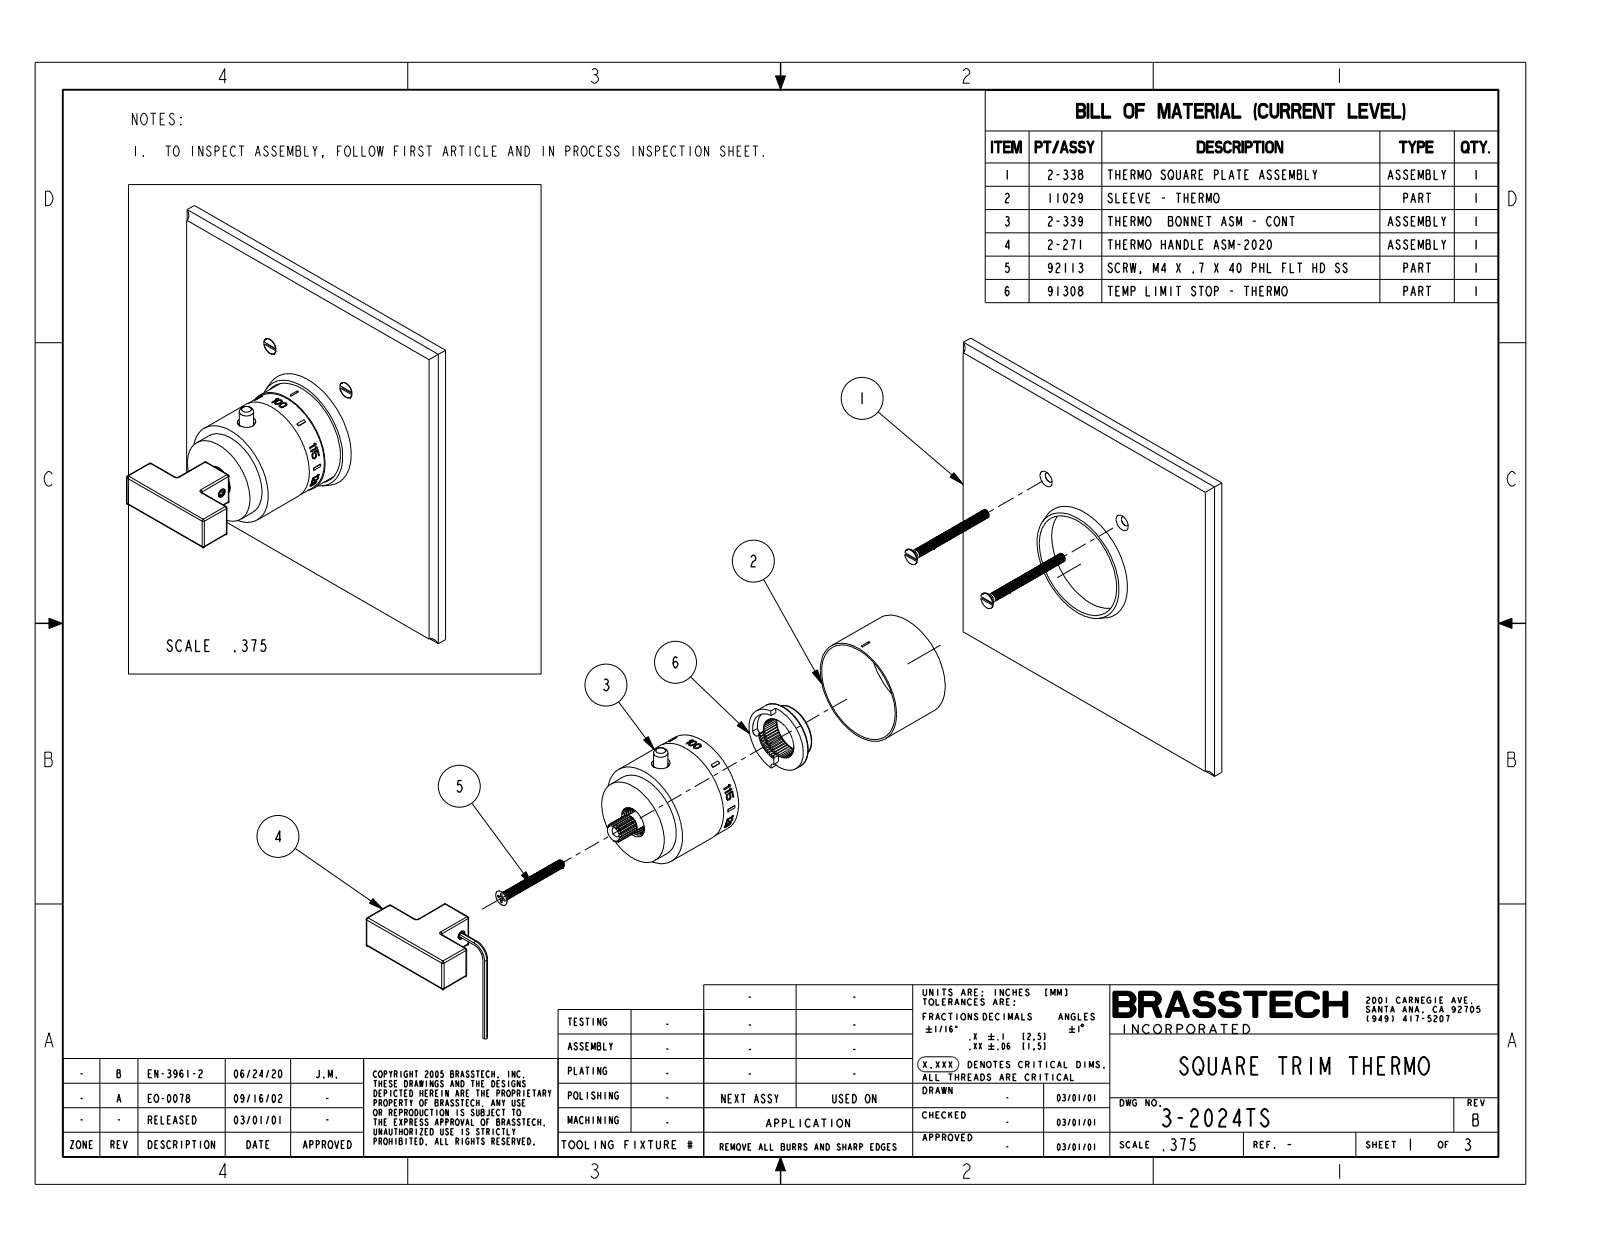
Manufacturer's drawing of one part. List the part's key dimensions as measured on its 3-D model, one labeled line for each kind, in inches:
Part name (STEP PRODUCT): 3-2024TS
STEP written by: CREO PARAMETRIC BY PTC INC, 2018400 (CONFIG_CONTROL_DESIGN)
Units: inches
Bodies: 1 solid, 422 faces (341 planar, 61 cylindrical, 20 other)
Overall size (bounding box): 6.5 × 6.5 × 4.024
Volume: 20.62 in³ · Surface area: 112.5 in²
Round bosses / shafts (diameter × count): ⌀1.97 ×1, ⌀1.94 ×1, ⌀1.929 ×1, ⌀1.615 ×1, ⌀0.4 ×1, ⌀0.26 ×1, ⌀0.067 ×1
Partial cylindrical surfaces — rounded edges, fillets, slot ends (radius × count): R0.03 ×22, R0.125 ×4, R0.969 ×1
Main face-to-face distances: 0.313, 3.563, 2.937, 6.5, 2.623, 2.31, 0.625, 4.024, 3.711, 1.401
